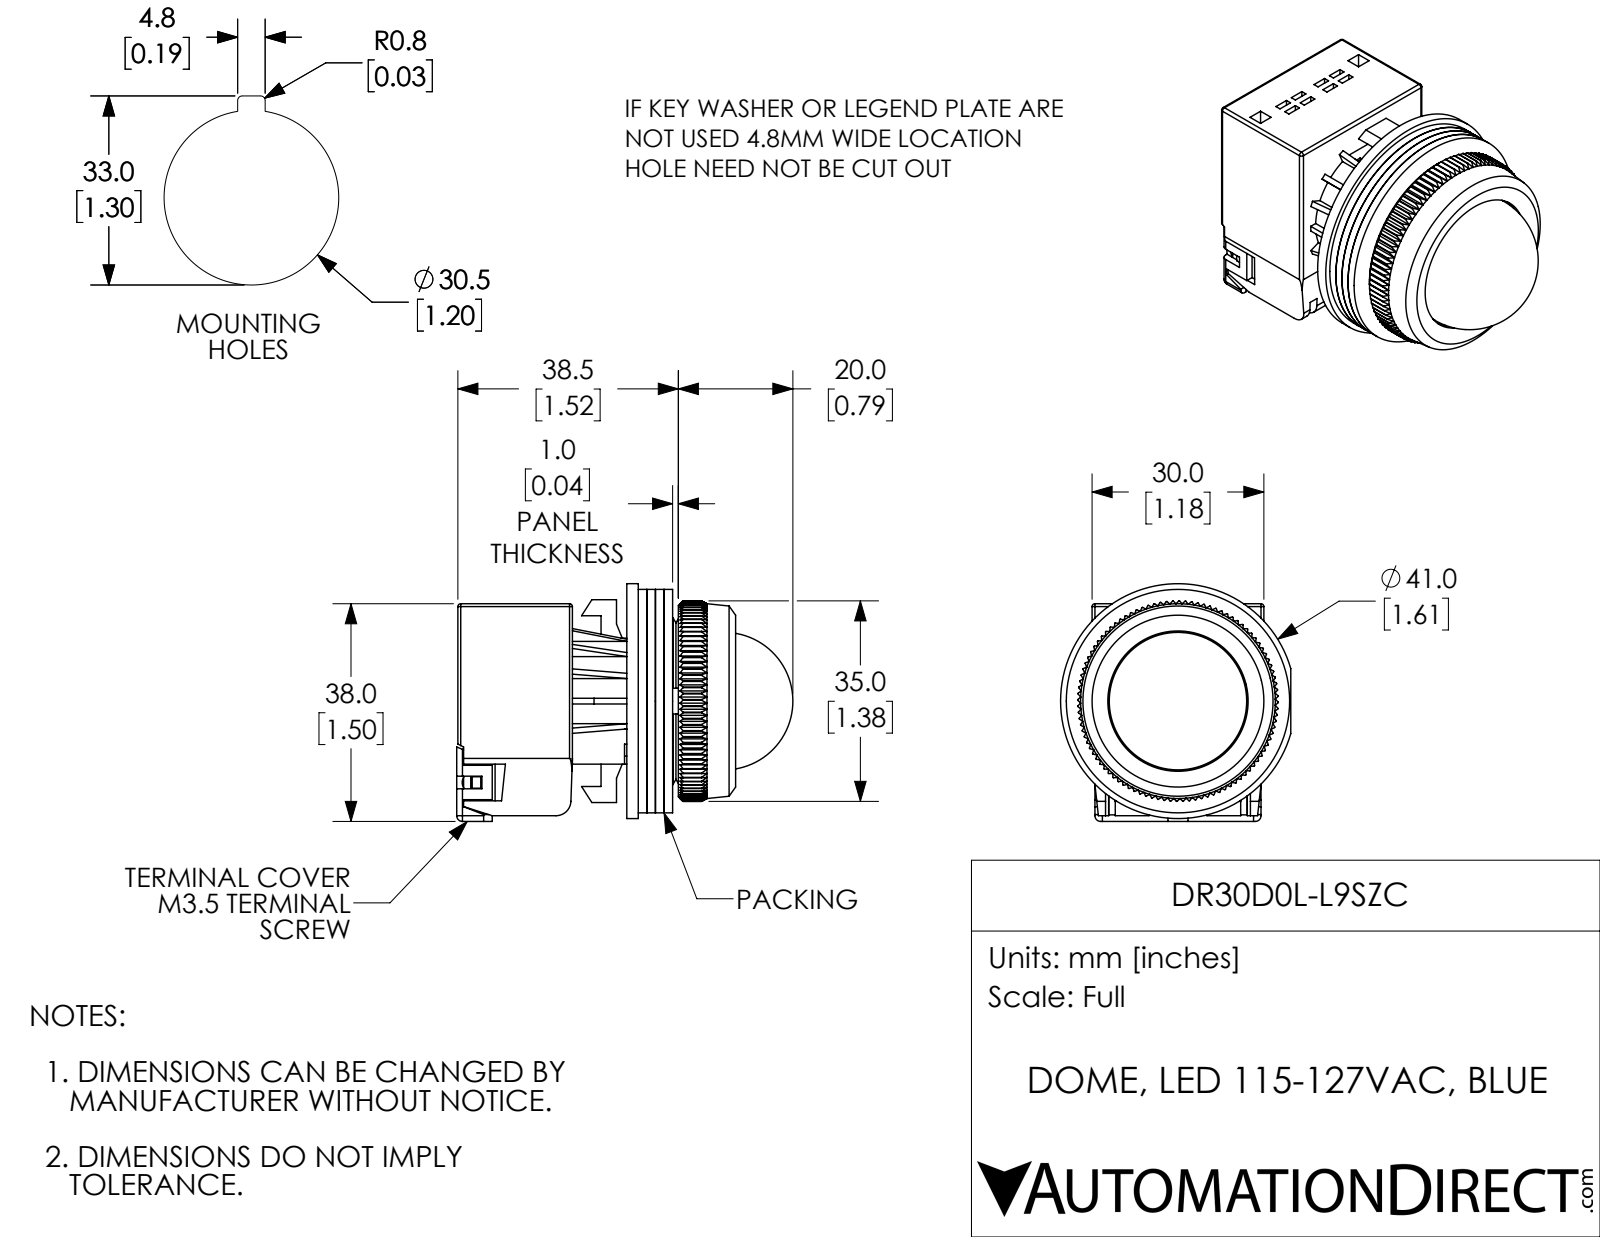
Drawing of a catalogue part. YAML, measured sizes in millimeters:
part_name: "DR30D0L-L9SZC"
step_written_by: "SolidWorks 2017 (AUTOMOTIVE_DESIGN)"
units: millimeters
bodies: {solids: 18, faces: 1544, planar: 945, cylindrical: 353, other: 246}
overall_size: [58.6, 41.5, 40.2]
volume: 35790
surface_area: 31430
round_holes:
  - {diameter: 3, count: 2}
  - {diameter: 3.1, count: 2}
  - {diameter: 3.5, count: 2}
  - {diameter: 7, count: 2}
  - {diameter: 9.2, count: 1}
  - {diameter: 11, count: 1}
  - {diameter: 11.7, count: 1}
  - {diameter: 13.8, count: 1}
  - {diameter: 14.3, count: 1}
  - {diameter: 14.8, count: 1}
  - {diameter: 16, count: 1}
  - {diameter: 18.3, count: 1}
round_bosses_or_shafts:
  - {diameter: 5.9, count: 2}
  - {diameter: 41, count: 1}
  - {diameter: 39, count: 1}
  - {diameter: 29.5, count: 1}
  - {diameter: 24, count: 1}
  - {diameter: 21.8, count: 1}
  - {diameter: 20.8, count: 1}
  - {diameter: 20.3, count: 1}
partial_cylinders:
  - {radius: 1, count: 14}
  - {radius: 0.2, count: 8}
  - {radius: 0.5, count: 8}
  - {radius: 1.7, count: 3}
  - {radius: 0.7, count: 1}
  - {radius: 1.7, count: 1}
  - {radius: 2, count: 1}
  - {radius: 2.6, count: 1}
face_to_face_distances: [1.5, 3, 4.5, 1, 8, 5, 13, 17.5, 9.5, 29.5]
hole_center_spacings: [17.9, 16]
